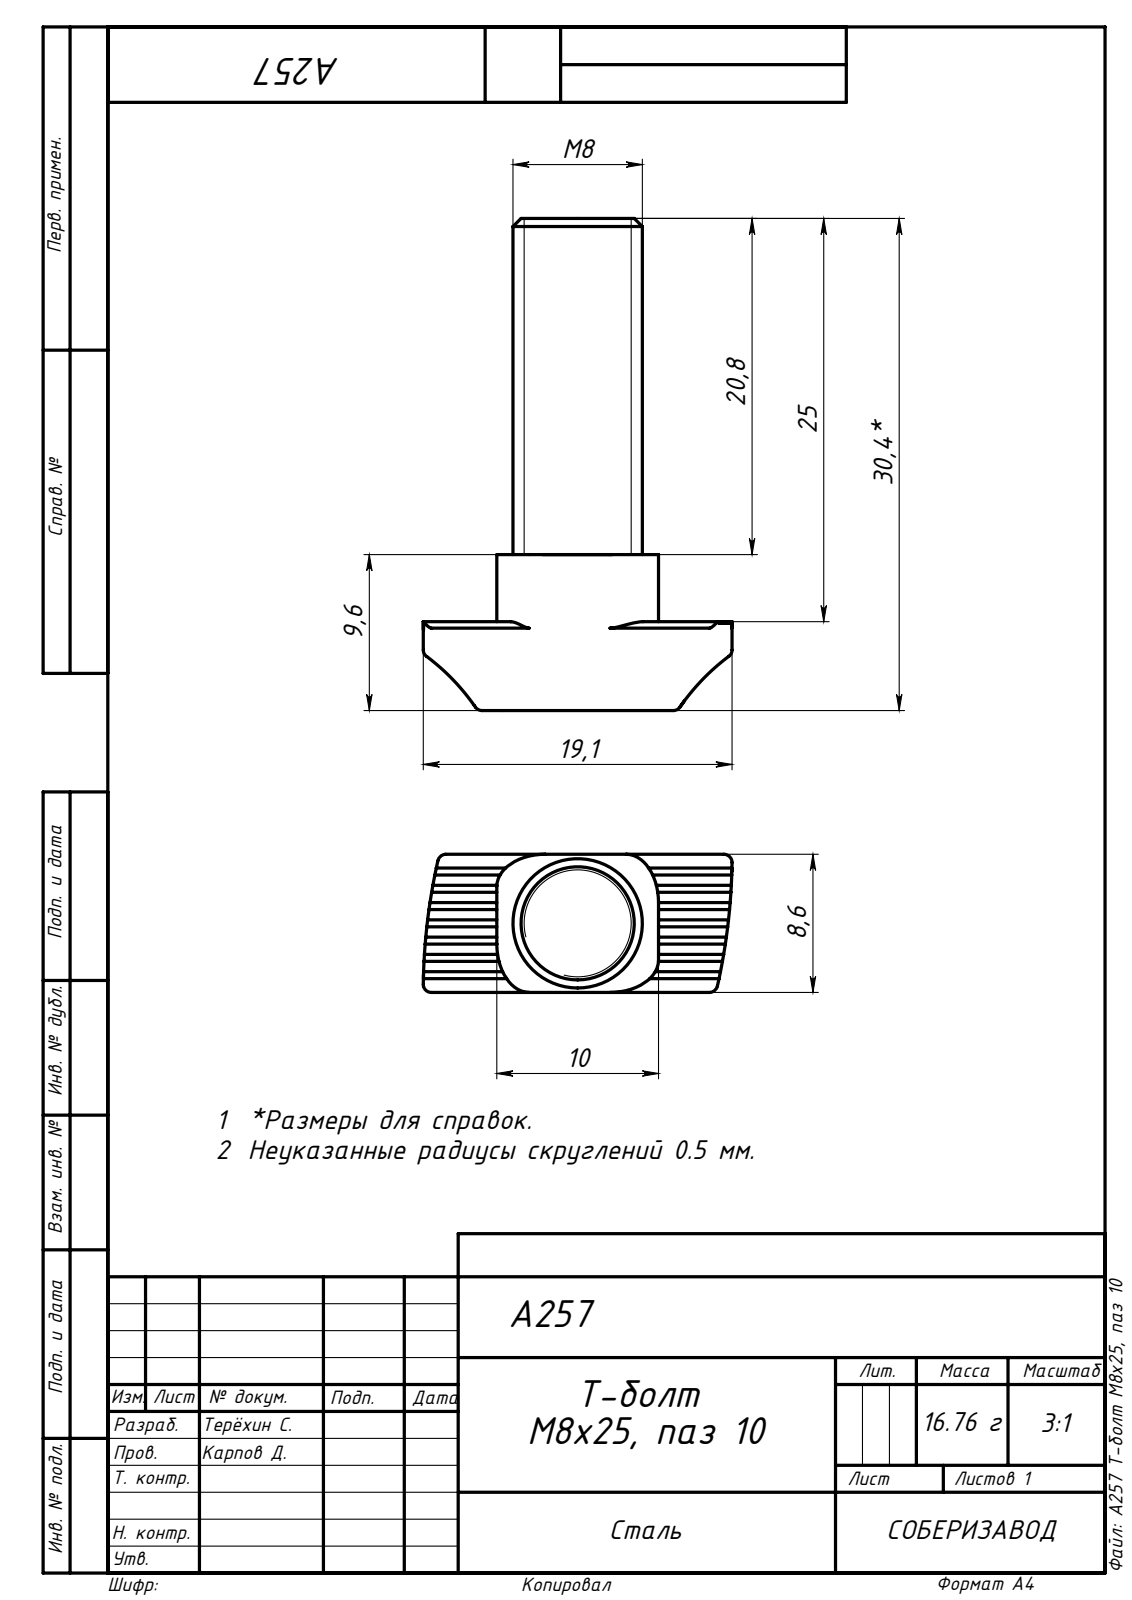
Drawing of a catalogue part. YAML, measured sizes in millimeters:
part_name: "A257 Т-болт М8х25, паз 10"
step_written_by: "SolidWorks 2020 (AUTOMOTIVE_DESIGN)"
units: millimeters
bodies: {solids: 1, faces: 77, planar: 27, cylindrical: 26, other: 24}
overall_size: [30.45, 19.09, 8.55]
volume: 2129
surface_area: 1188
round_bosses_or_shafts:
  - {diameter: 8, count: 1}
partial_cylinders:
  - {radius: 0.56, count: 8}
  - {radius: 0.5, count: 6}
  - {radius: 37.05, count: 2}
face_to_face_distances: [8.55, 30.45, 9.65, 20.8, 5.4, 4.25, 25.05, 10, 4.53, 14.53]
